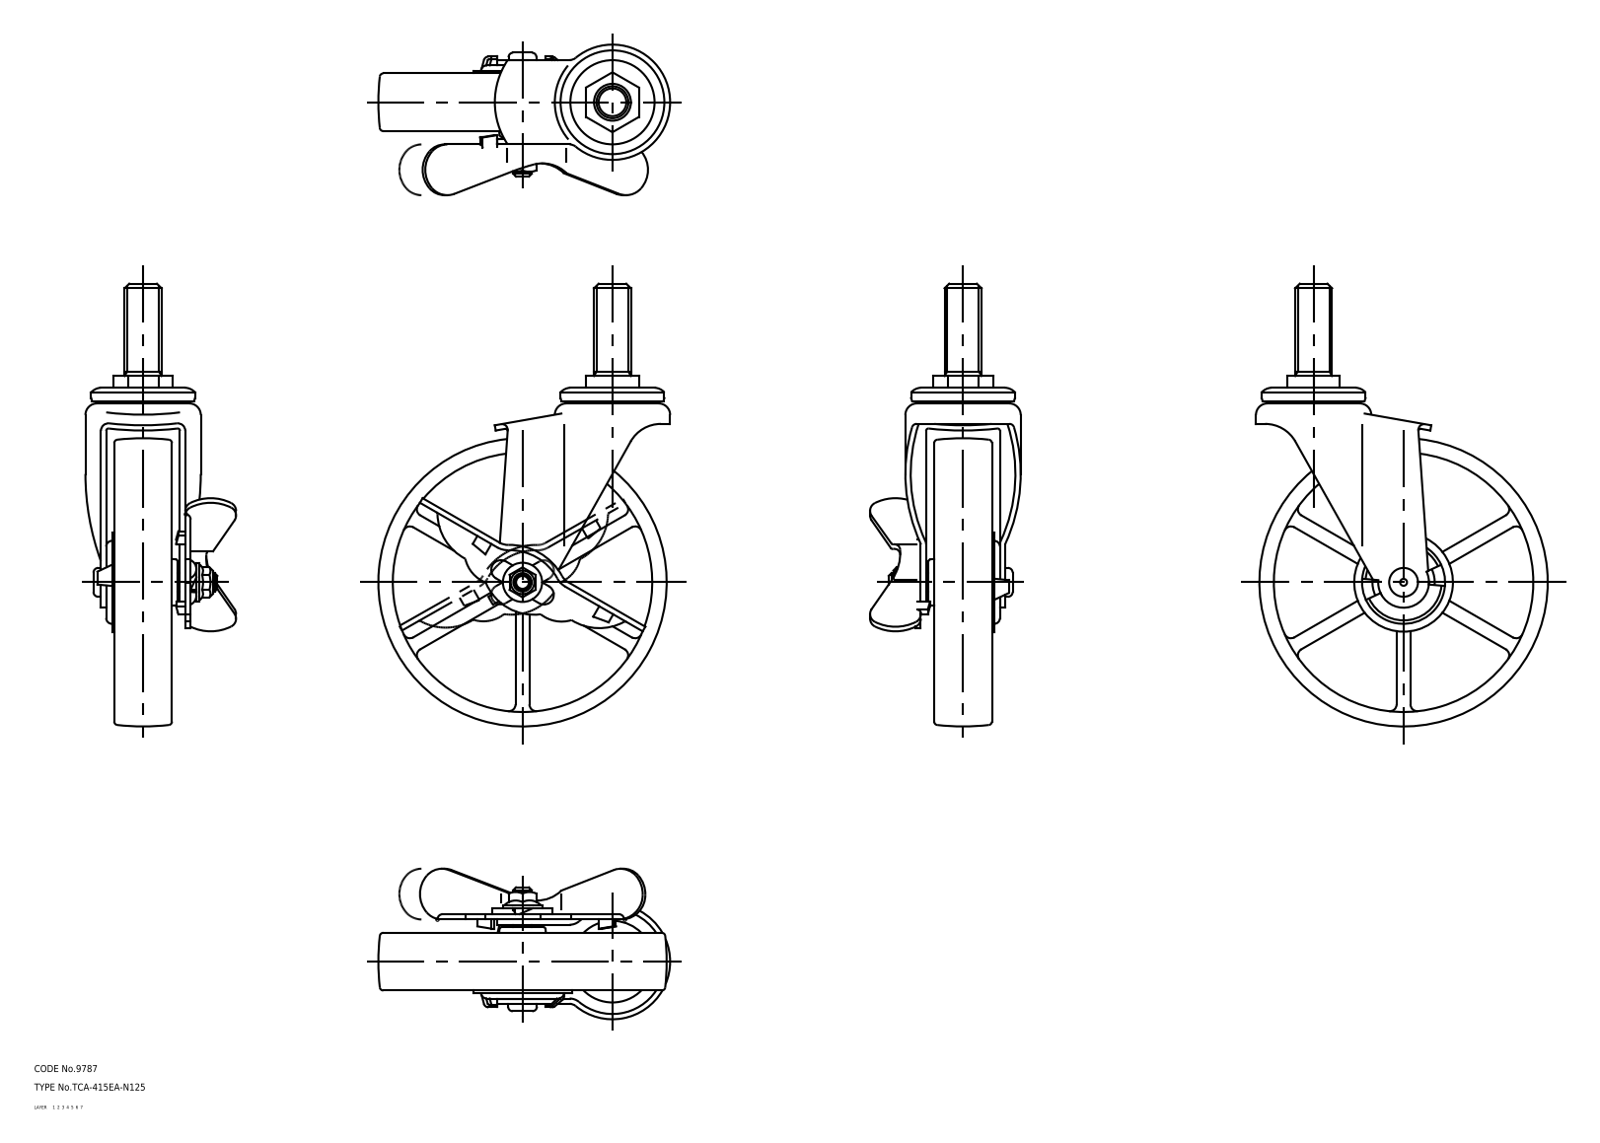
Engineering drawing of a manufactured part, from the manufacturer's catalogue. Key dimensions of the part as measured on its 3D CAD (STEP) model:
Part name (STEP PRODUCT): wheel; mounting plate; main shaft; lever (+2 more)
STEP written by: CADfix (AUTOMOTIVE_DESIGN)
Units: millimetres
Bodies: 6 solids, 597 faces (0 planar, 0 cylindrical, 597 other)
Overall size (bounding box): 192 × 126.5 × 65.3
Volume: 274 586 mm³ · Surface area: 81 988 mm²
